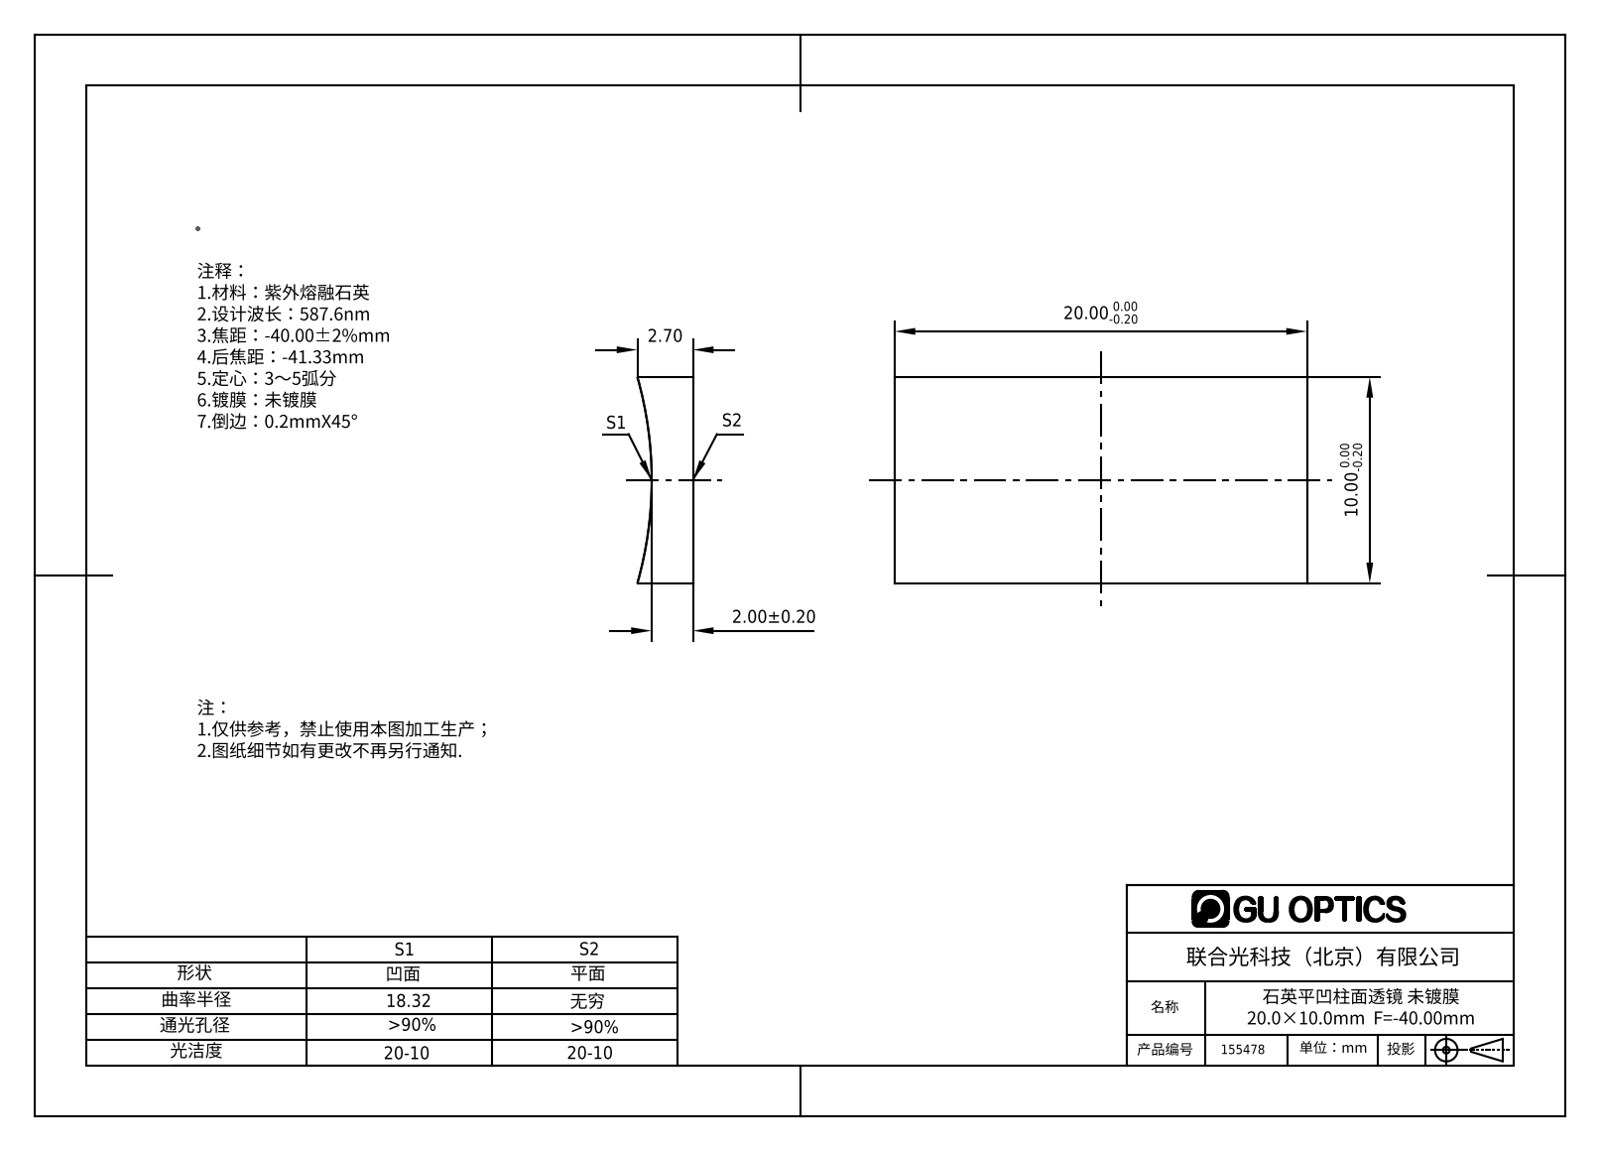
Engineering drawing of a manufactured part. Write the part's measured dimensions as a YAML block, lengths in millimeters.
part_name: "155478"
step_written_by: "SolidWorks 2016 (AUTOMOTIVE_DESIGN)"
units: millimeters
bodies: {solids: 1, faces: 6, planar: 5, cylindrical: 1, other: 0}
overall_size: [20, 10, 2.7]
volume: 446
surface_area: 555
partial_cylinders:
  - {radius: 18.32, count: 1}
face_to_face_distances: [10, 20]
